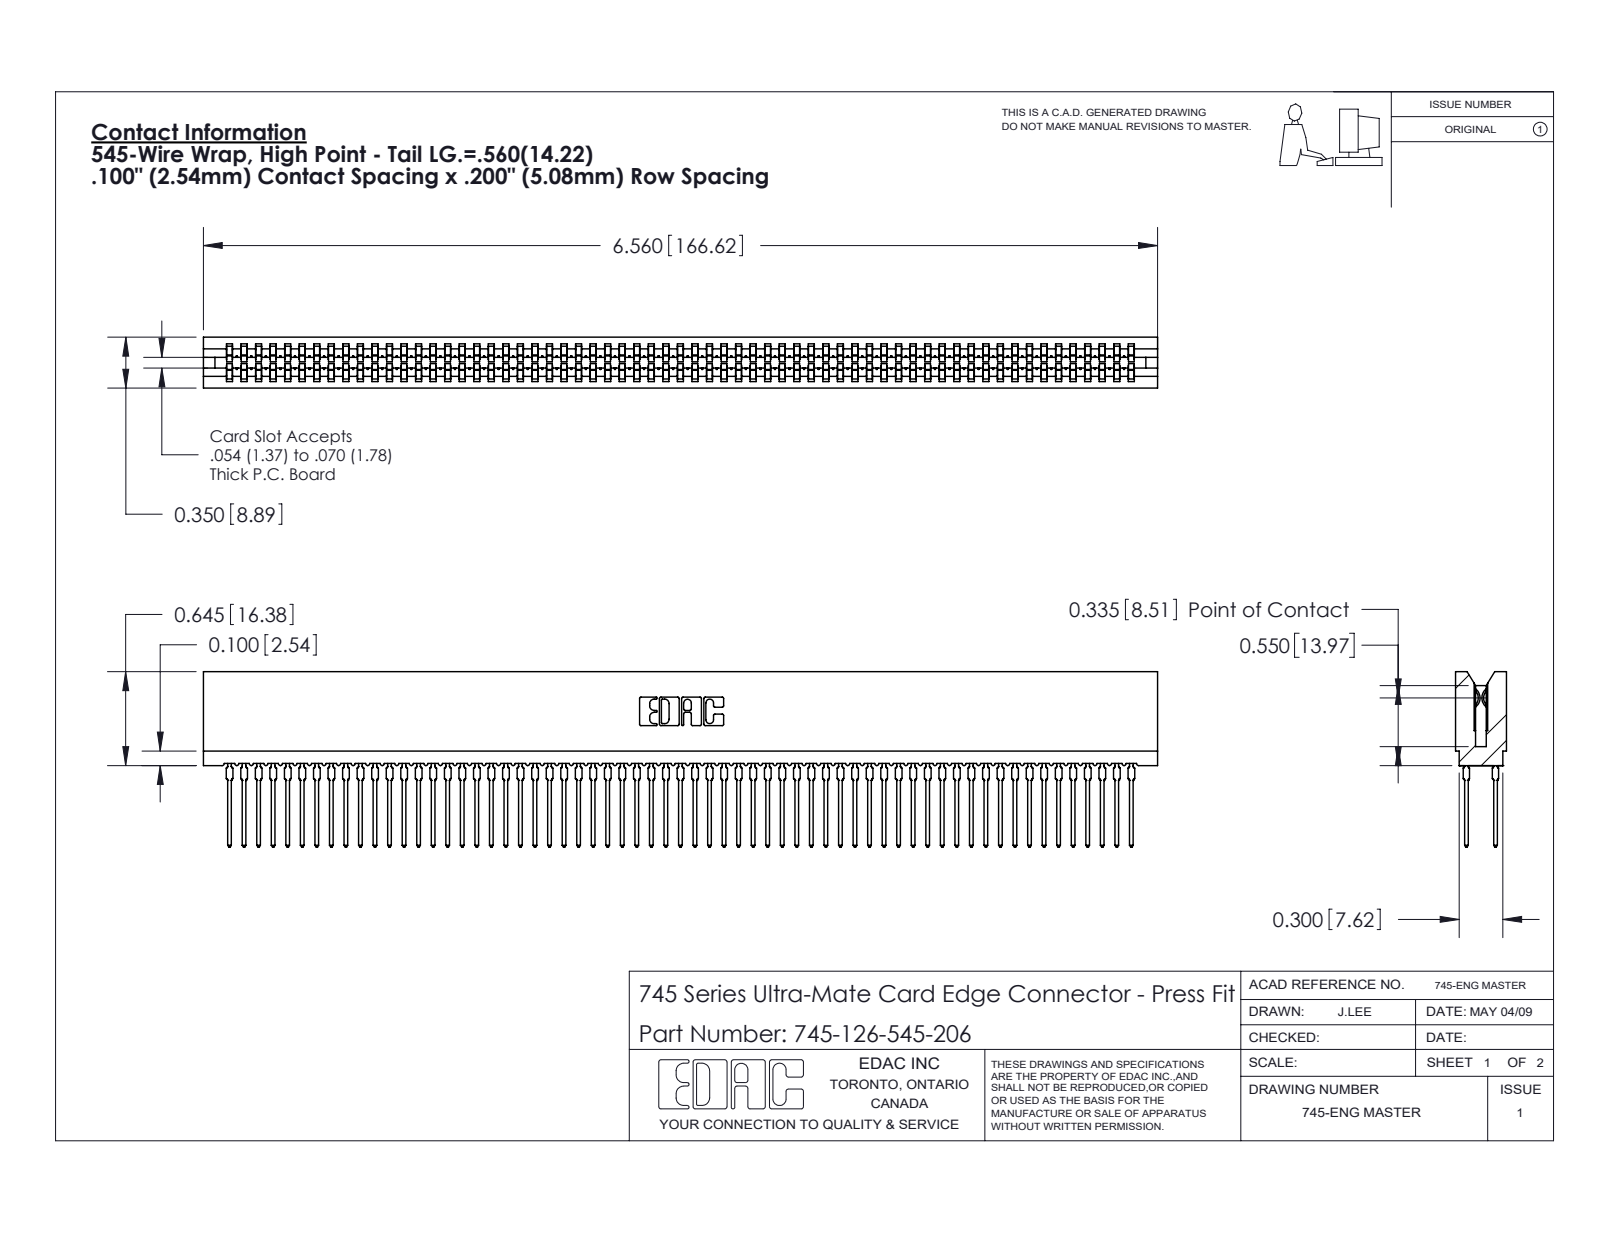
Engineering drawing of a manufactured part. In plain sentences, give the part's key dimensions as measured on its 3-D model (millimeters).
The part is named "745-292-001_545; 745 Part_Insulator Option - 06; 745-126-545-206". Its 3-D file was written by "SolidWorks 2020 (CONFIG_CONTROL_DESIGN)". It is 127 solids with 11373 faces: 5852 planar, 2245 cylindrical and 3276 other. Overall it measures 166.6 by 30.6 by 8.9 millimeters. Its volume is 15 300 cubic millimeters and its surface area 33 540 square millimeters. Partial cylindrical surfaces (rounded edges, fillets, slot ends): 252 of radius 0.5, 126 of radius 0.4, 22 of radius 0.3, 8 of radius 0.1, 8 of radius 0.3, 6 of radius 0.2, 6 of radius 0.8, 3 of radius 0.7. The main face-to-face distances are 1.6, 7.3, 8.9, 1.1, 7.7, 0.5, 6.2, 3.5, 5.4, 2.4.
